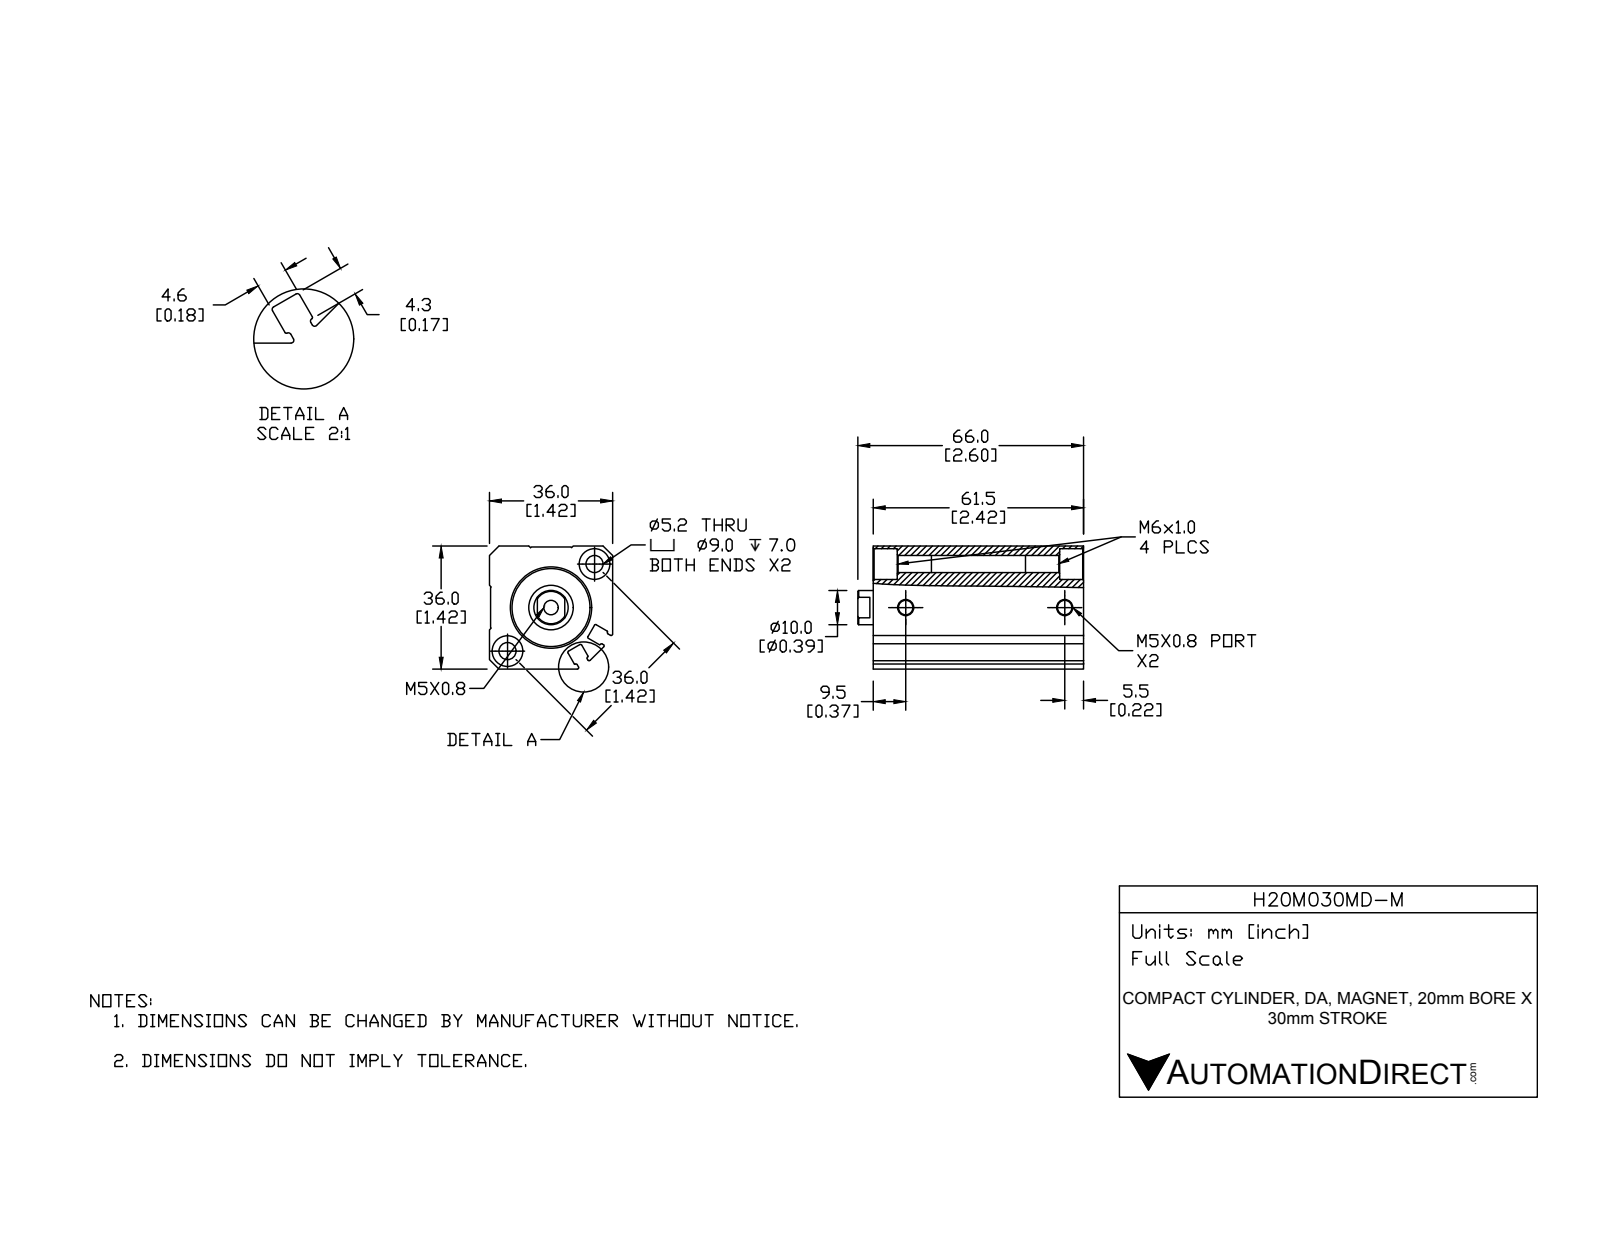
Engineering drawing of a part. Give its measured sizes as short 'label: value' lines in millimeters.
name: H20M030MD-M-BODY; H20M030MD-M; H20M030MD-M-PISTON
written by: SolidWorks 2015 (CONFIG_CONTROL_DESIGN)
unit: mm
bodies: 2 solids, 141 faces (53 planar, 55 cylindrical, 33 other)
size: 66 × 36 × 36
volume: 60 836 mm³; area: 21 878 mm²
holes: 3× ⌀4.2, 2× ⌀5, 2× ⌀9, 1× ⌀10, 1× ⌀13, 1× ⌀20, 1× ⌀22.8
bosses: 1× ⌀11
rounds: 12× R0.4, 4× R0.2
face distances: 36, 35.7, 4, 61.5, 57.5, 4.6, 2.6, 1.4, 60.1, 50.5
hole spacings: 18, 36.01, 46.5
